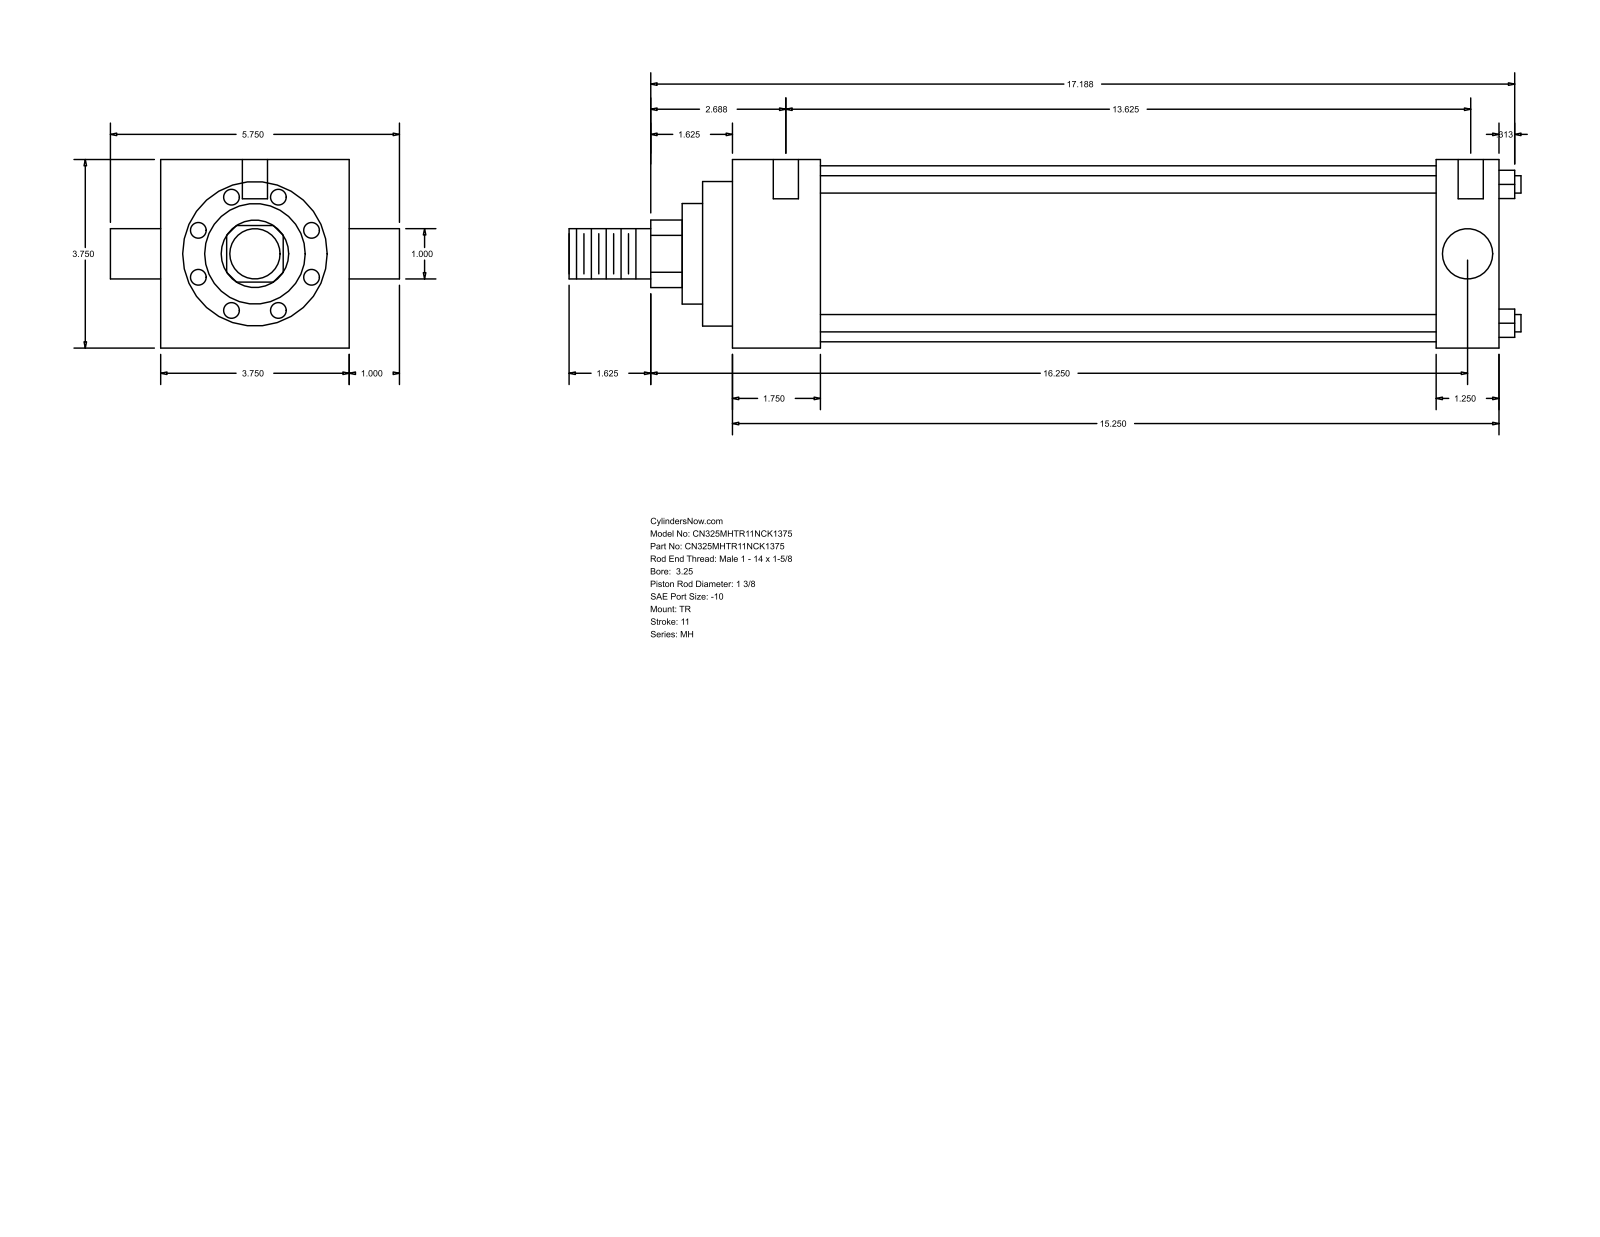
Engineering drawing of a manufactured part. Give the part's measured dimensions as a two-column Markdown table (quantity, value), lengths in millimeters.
| quantity | value |
| --- | --- |
| part name | MH_TR__0325_1.375 |
| STEP written by | GSSL Pune (CONFIG_CONTROL_DESIGN) |
| units | millimeters |
| bodies | 0 solids, 86 faces (61 planar, 25 cylindrical, 0 other) |
| overall size | 481.01 × 146.05 × 95.25 |
| round holes (diameter × count) | 5.56 × 3, 12.7 × 2 |
| round bosses / shafts (diameter × count) | 8.76 × 4, 25.4 × 2, 88.9 × 1, 73.03 × 1, 50.8 × 1, 34.92 × 1 |
| partial cylindrical surfaces (radius × count) | 17.06 × 1 |
| main face-to-face distances | 95.24, 387.35, 44.45, 355.61, 311.16, 342.9, 31.74, 15.08, 59.53, 370.69 |
| hole center spacings | 1.59, 4.76, 346.08, 347.67, 350.84, 352.43 |
